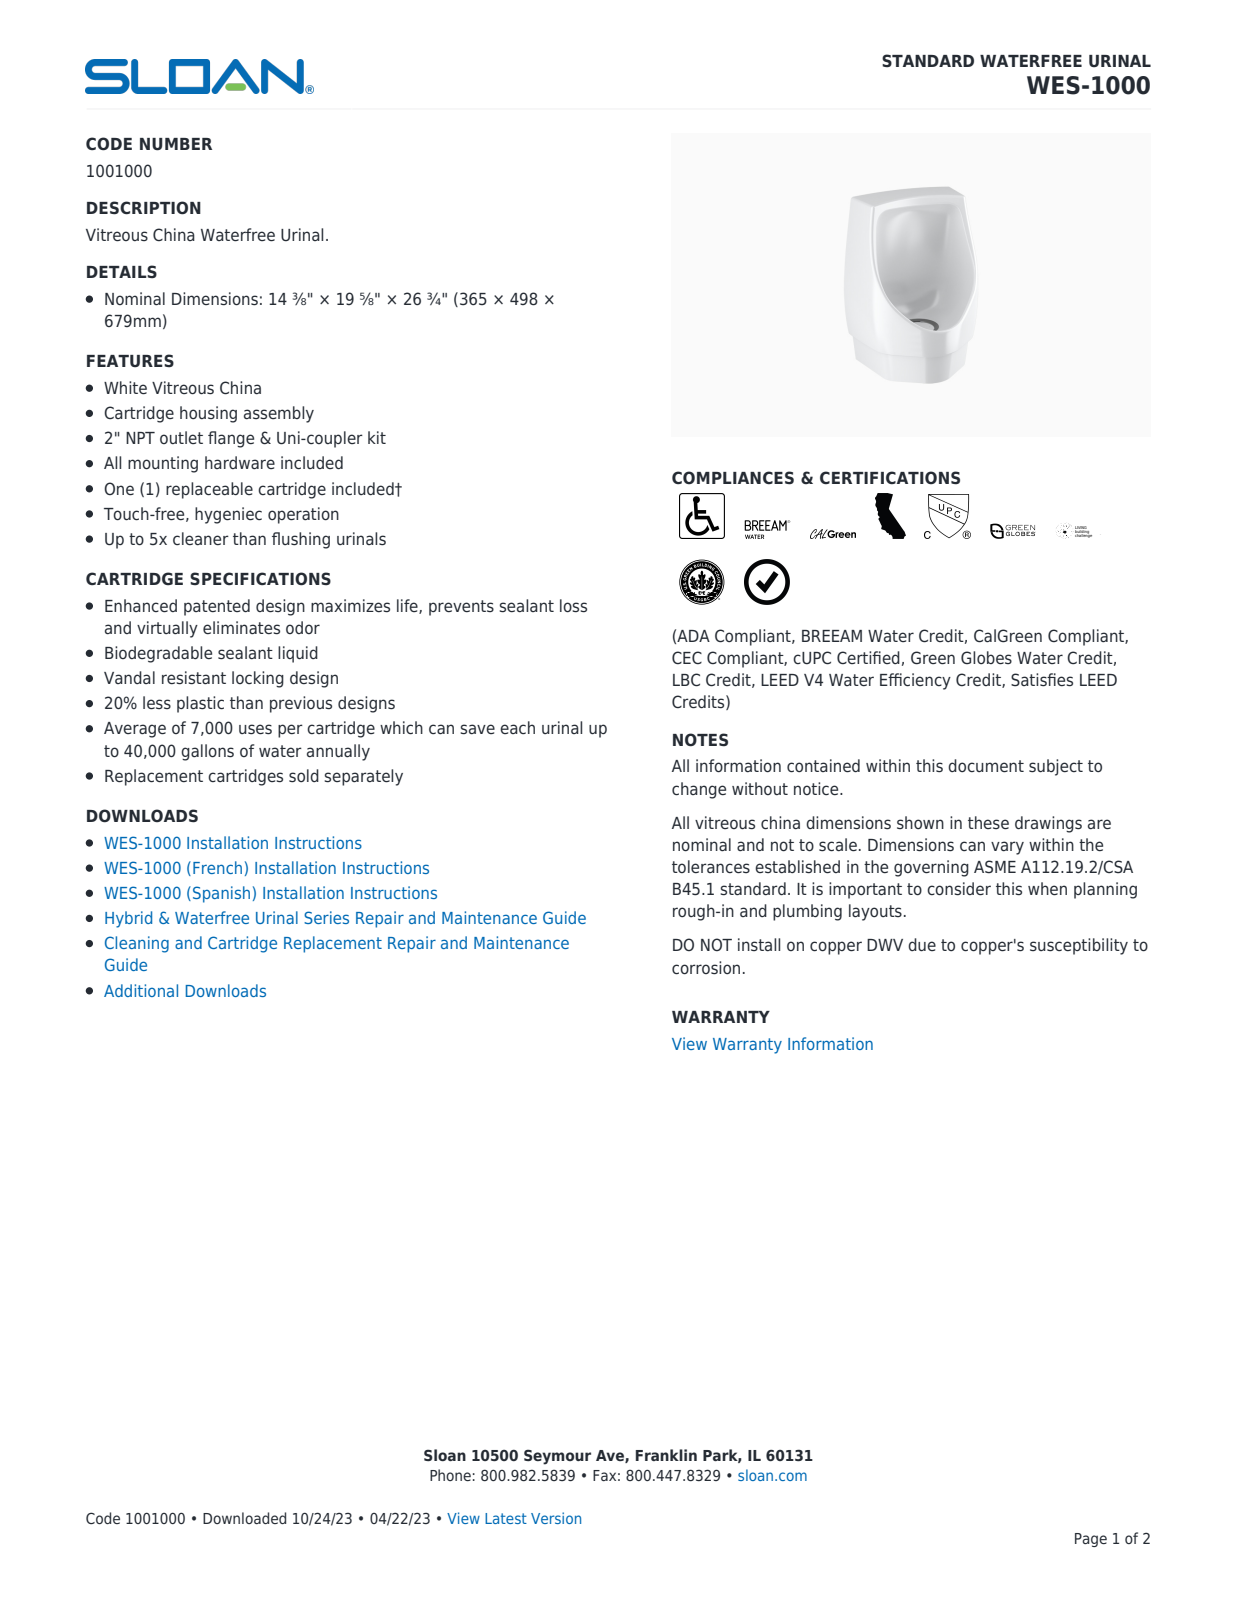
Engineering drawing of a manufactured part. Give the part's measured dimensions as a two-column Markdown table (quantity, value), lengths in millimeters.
| quantity | value |
| --- | --- |
| STEP written by | ACIS (automotive_design) |
| units | millimeters |
| bodies | 2 solids, 24 faces (4 planar, 10 cylindrical, 10 other) |
| overall size | 44.5 × 3.5 × 3.5 |
| volume | 339 mm³ |
| surface area | 538 mm² |
| round holes (diameter × count) | 1.35 × 1 |
| round bosses / shafts (diameter × count) | 3.5 × 1, 2.18 × 1 |
| main face-to-face distances | 33.4, 11.1, 44.5 |
